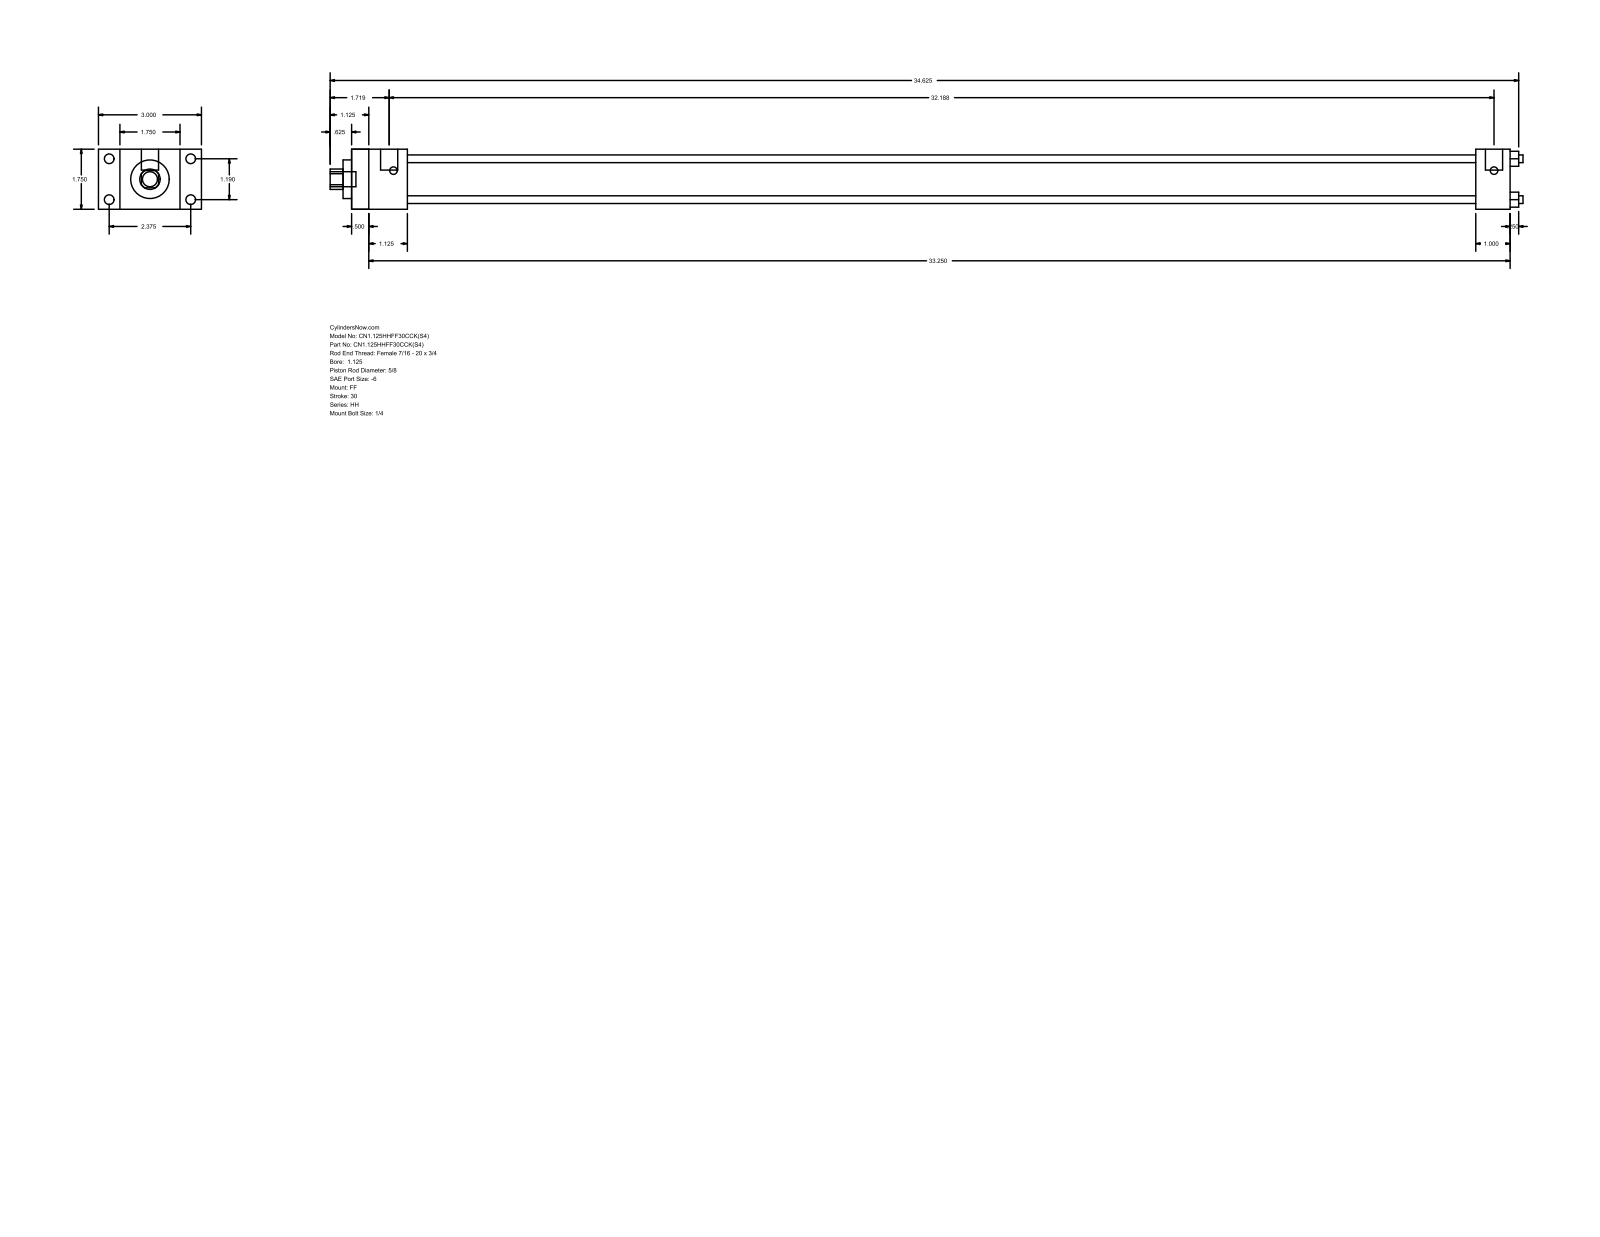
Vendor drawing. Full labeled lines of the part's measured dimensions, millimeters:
Part name (STEP PRODUCT): HH_FF__0112_0.625
STEP written by: GSSL Pune (CONFIG_CONTROL_DESIGN)
Units: millimetres
Bodies: 0 solids, 92 faces (64 planar, 28 cylindrical, 0 other)
Overall size (bounding box): 882.65 × 76.2 × 44.45
Round holes (diameter × count): ⌀5.71 ×4, ⌀15.88 ×1, ⌀28.57 ×1, ⌀34.92 ×1
Round bosses / shafts (diameter × count): ⌀7.14 ×4, ⌀5.56 ×4, ⌀12.7 ×2, ⌀11.11 ×1
Partial cylindrical surfaces — rounded edges, fillets, slot ends (radius × count): R7.54 ×1
Main face-to-face distances: 44.46, 857.24, 12.69, 844.55, 15.87, 60.33, 28.58, 41.27, 831.85, 819.16
Hole centre spacings: 21.37, 30.22, 42.74
